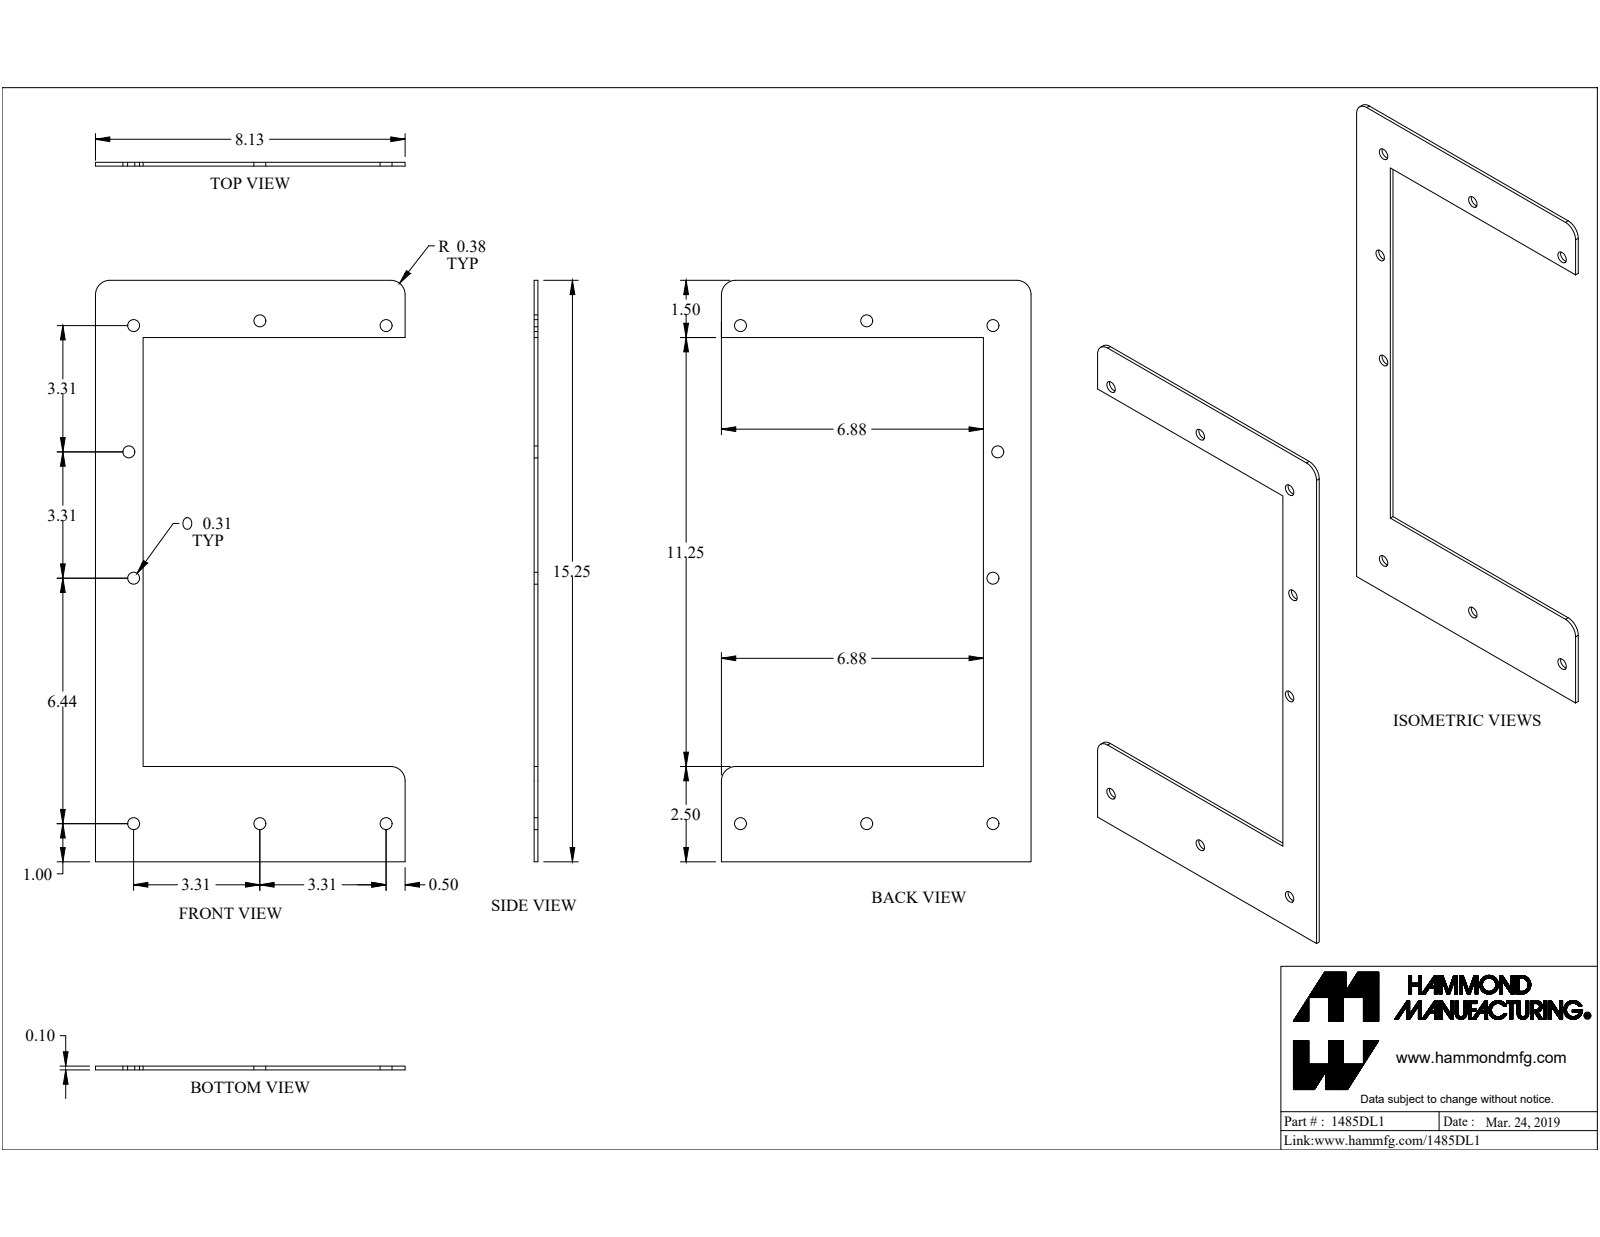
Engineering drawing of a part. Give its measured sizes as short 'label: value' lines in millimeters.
name: 1485DL1
written by: SolidWorks 2019 (CONFIG_CONTROL_DESIGN)
unit: mm
bodies: 1 solid, 21 faces (10 planar, 11 cylindrical, 0 other)
size: 387.4 × 206.4 × 2.5
volume: 75 150 mm³; area: 63 550 mm²
holes: 8× ⌀8
rounds: 3× R9.5
face distances: 2.5, 31.8, 387.4, 38.1, 349.3, 323.9, 285.8, 63.5, 206.4, 174.6
hole spacings: 84.2, 168.3, 84.2, 191, 331.8, 342.3, 345.4, 372
